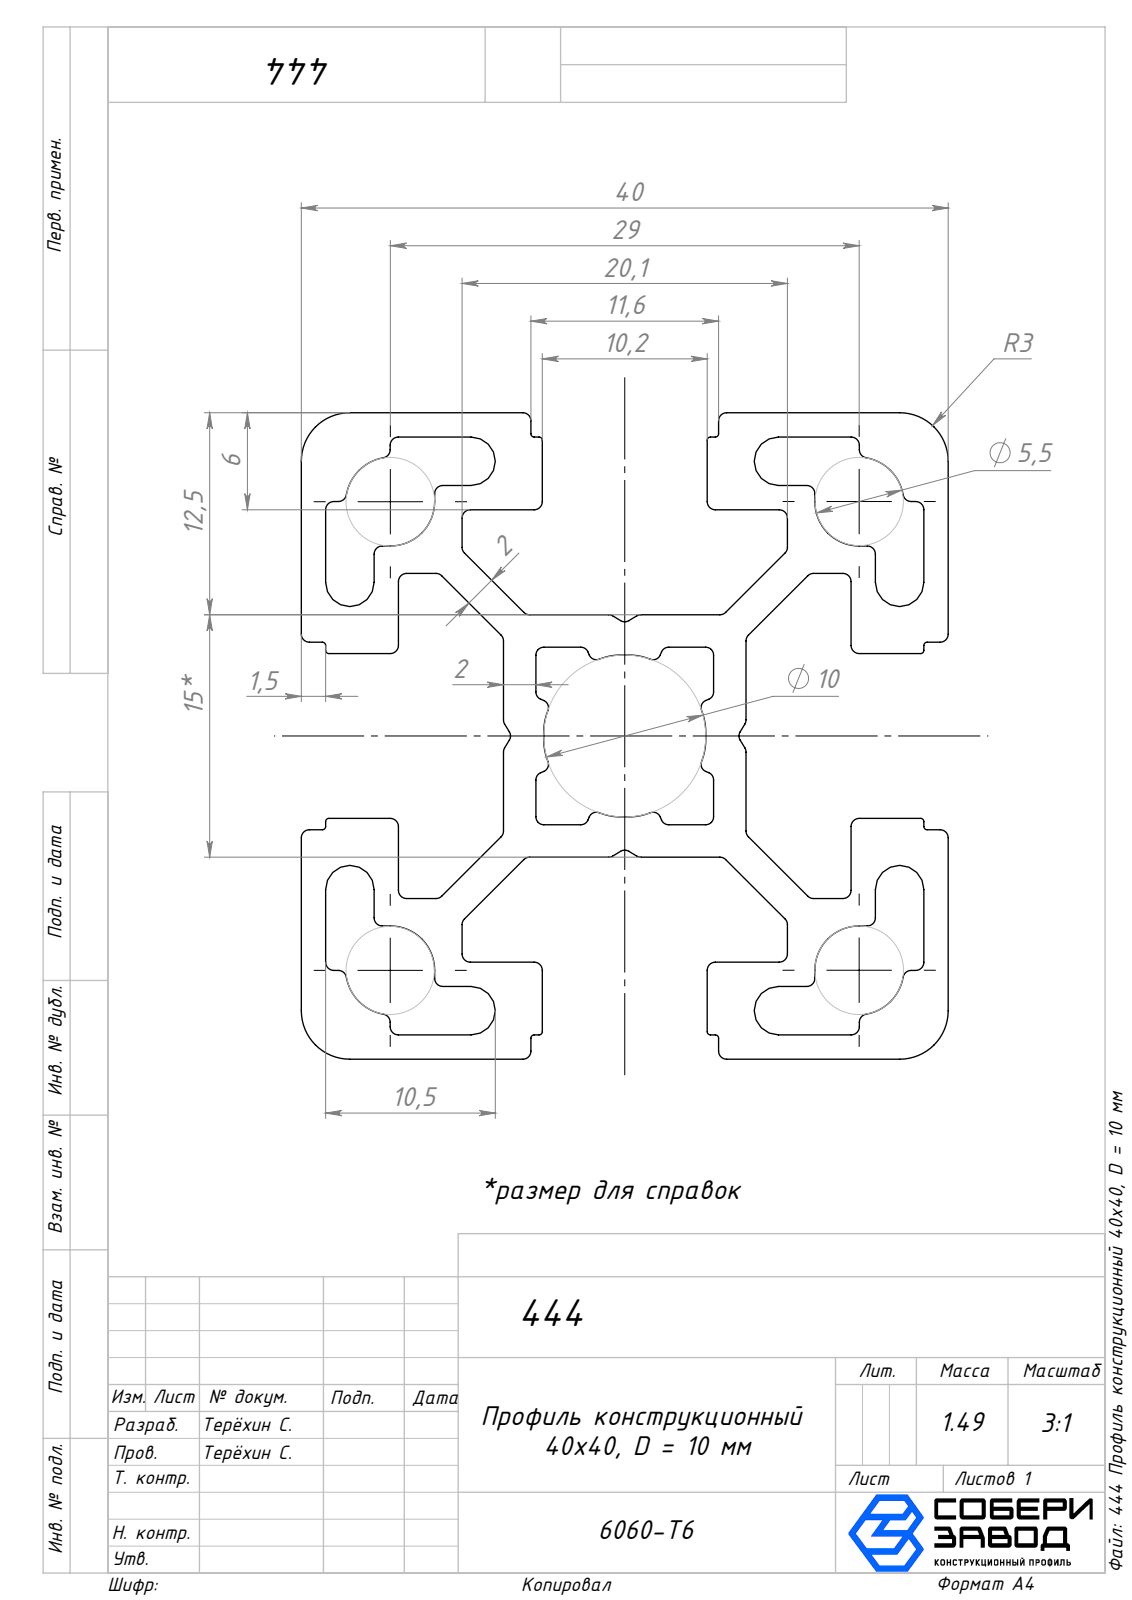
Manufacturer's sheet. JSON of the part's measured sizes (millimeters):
{"part_name": "444 Профиль конструкционный 40х40, Ф = 10 мм; 444 Профиль конструкционный 40х40, Ф = 10 мм_00", "step_written_by": "SolidWorks 2025 (CONFIG_CONTROL_DESIGN)", "units": "millimeters", "bodies": {"solids": 1, "faces": 294, "planar": 122, "cylindrical": 172, "other": 0}, "overall_size": [1000, 40, 40], "volume_mm3": 550002, "surface_area_mm2": 500212, "partial_cylinders_radius": [[0.51, 32], [0.2, 16], [0.48, 8], [0.48, 8], [0.48, 8], [0.49, 8], [0.5, 8], [0.5, 8]], "face_to_face_distances": [40, 12.5, 27.5, 1.5, 11, 26, 38.5, 33.99, 32.49, 6.01]}
